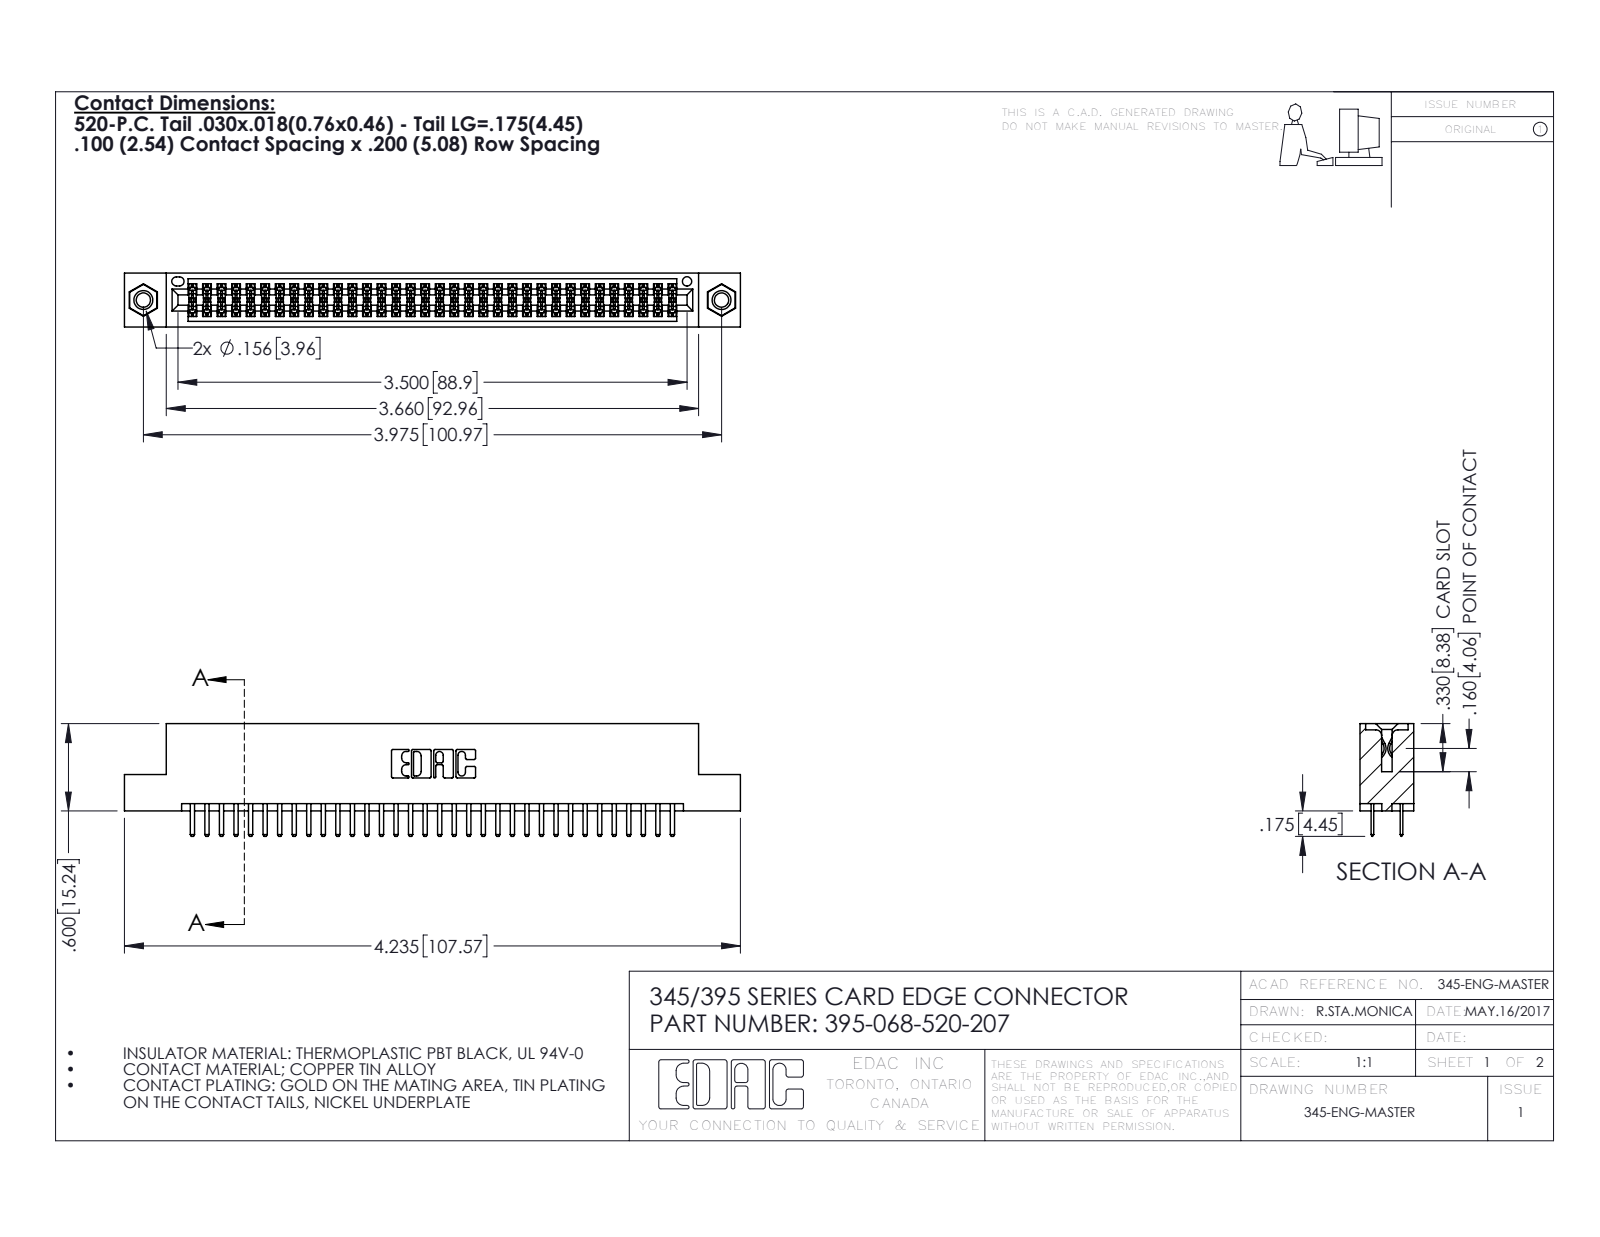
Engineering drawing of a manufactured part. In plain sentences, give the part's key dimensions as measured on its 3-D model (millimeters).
The part is named "395-068-520-207; 345 Part_Flush Mounting Lugs - 0.156 Dia-TI; 345-250-001_345-250-005-103; 345-292-001_345-293-120". Its 3-D file was written by "SolidWorks 2016 (CONFIG_CONTROL_DESIGN)". It is 71 solids with 3858 faces: 2492 planar, 1350 cylindrical and 16 other. Overall it measures 107.6 by 19.7 by 9.4 millimeters. Its volume is 10 300 cubic millimeters and its surface area 15 080 square millimeters. Round holes: 2 of diameter 2.5, 2 of diameter 3.2, 2 of diameter 4, 1 of diameter 1.6. Round bosses or shafts: 2 of diameter 3.9. Partial cylindrical surfaces (rounded edges, fillets, slot ends): 102 of radius 0.2, 72 of radius 0.3, 22 of radius 0.3, 6 of radius 0.2, 6 of radius 0.8, 3 of radius 0.7, 2 of radius 0.4, 2 of radius 0.5. The main face-to-face distances are 1.8, 7.6, 5.1, 9.4, 2.5, 6.9, 0.6, 5.7, 0.6, 1.8. The hole center spacings are 6.9, 95, 101.
